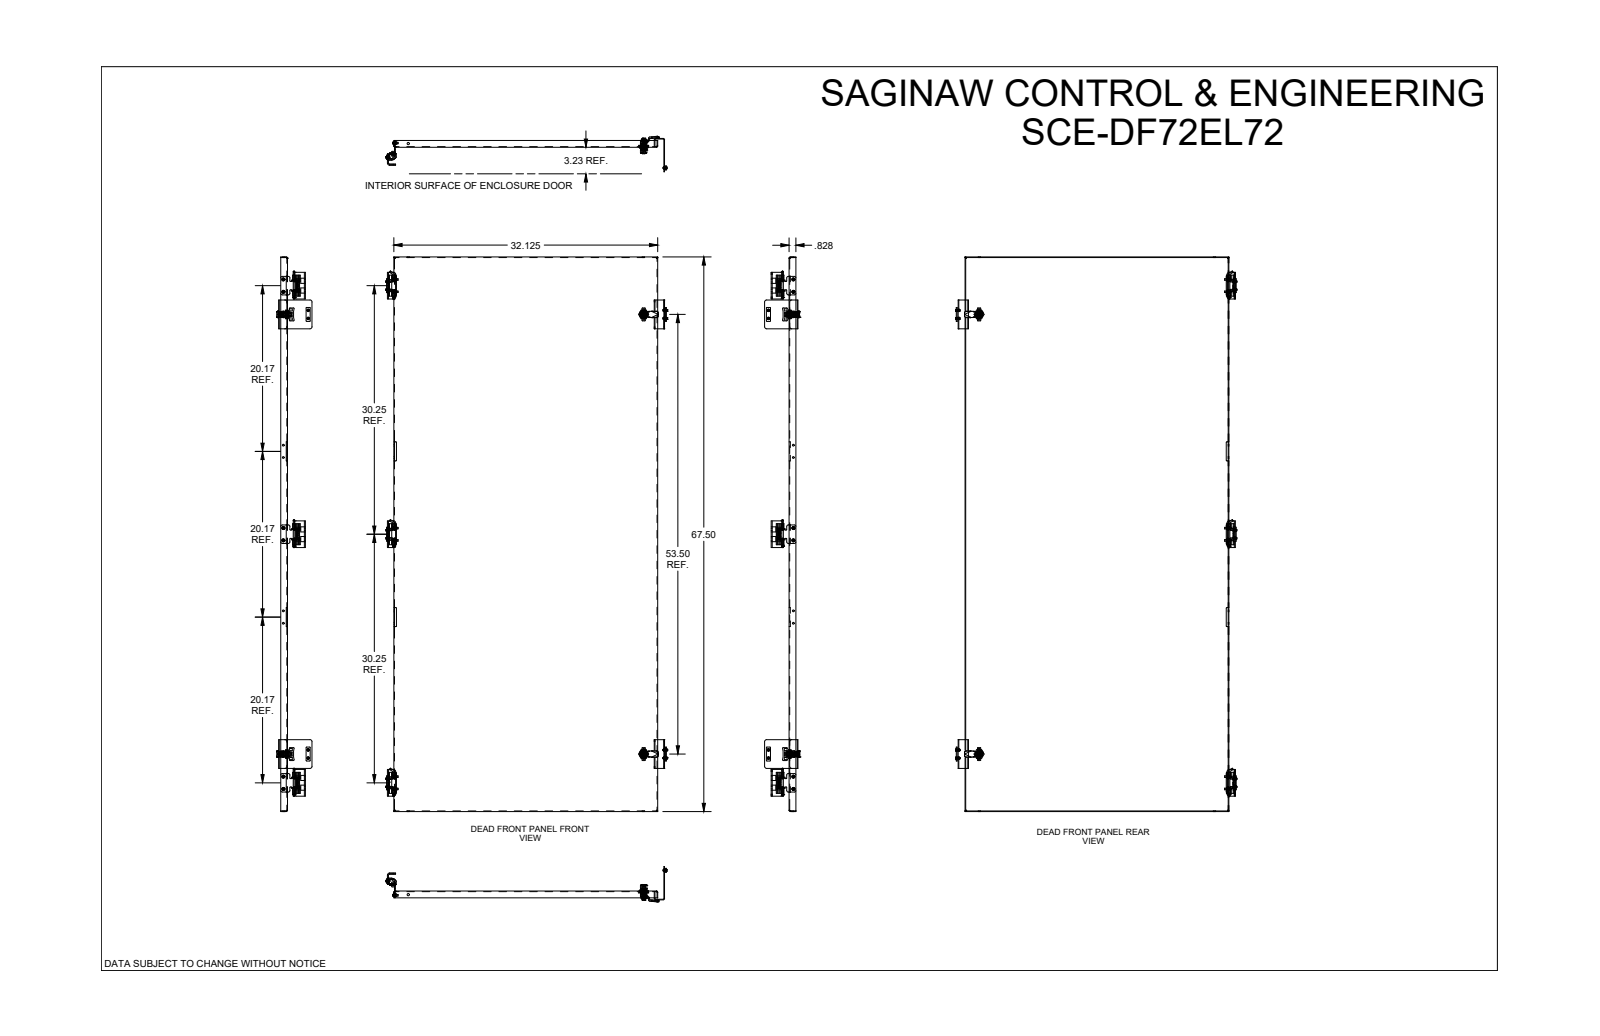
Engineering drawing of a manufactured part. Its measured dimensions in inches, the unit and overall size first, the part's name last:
Units: inches
Overall size (bounding box): 67.5 × 34.243 × 4.319
Round holes (diameter × count): ⌀0.172 ×10, ⌀0.244 ×10, ⌀0.19 ×6, ⌀0.21 ×6, ⌀0.25 ×6, ⌀0.266 ×6, ⌀0.197 ×2, ⌀0.315 ×2, ⌀0.394 ×2, ⌀0.433 ×2, ⌀0.634 ×2, ⌀0.222 ×1
Round bosses / shafts (diameter × count): ⌀0.25 ×10, ⌀0.17 ×10, ⌀0.373 ×6, ⌀0.34 ×6, ⌀0.249 ×6, ⌀0.188 ×6, ⌀0.196 ×4, ⌀1.102 ×2
Partial cylindrical surfaces — rounded edges, fillets, slot ends (radius × count): R0.012 ×54, R0.02 ×22, R0.062 ×22, R0.25 ×21, R0.157 ×16, R0.068 ×9, R0.04 ×8, R0.059 ×8
Main face-to-face distances: 0.06, 0.06, 32.065, 0.078, 32.125, 32.005, 67.44, 32.882, 32.822, 0.817
Hole centre spacings: 30.25, 0.985, 1.749, 1.75, 2.13, 2.13, 60.5, 29.059
Volume: 151.1 in³ · Surface area: 4 906 in²
Bodies: 54 solids, 2129 faces (1082 planar, 636 cylindrical, 411 other)
Part name (STEP PRODUCT): SCE-DF72EL72
STEP written by: SolidWorks 2021 (AUTOMOTIVE_DESIGN)
